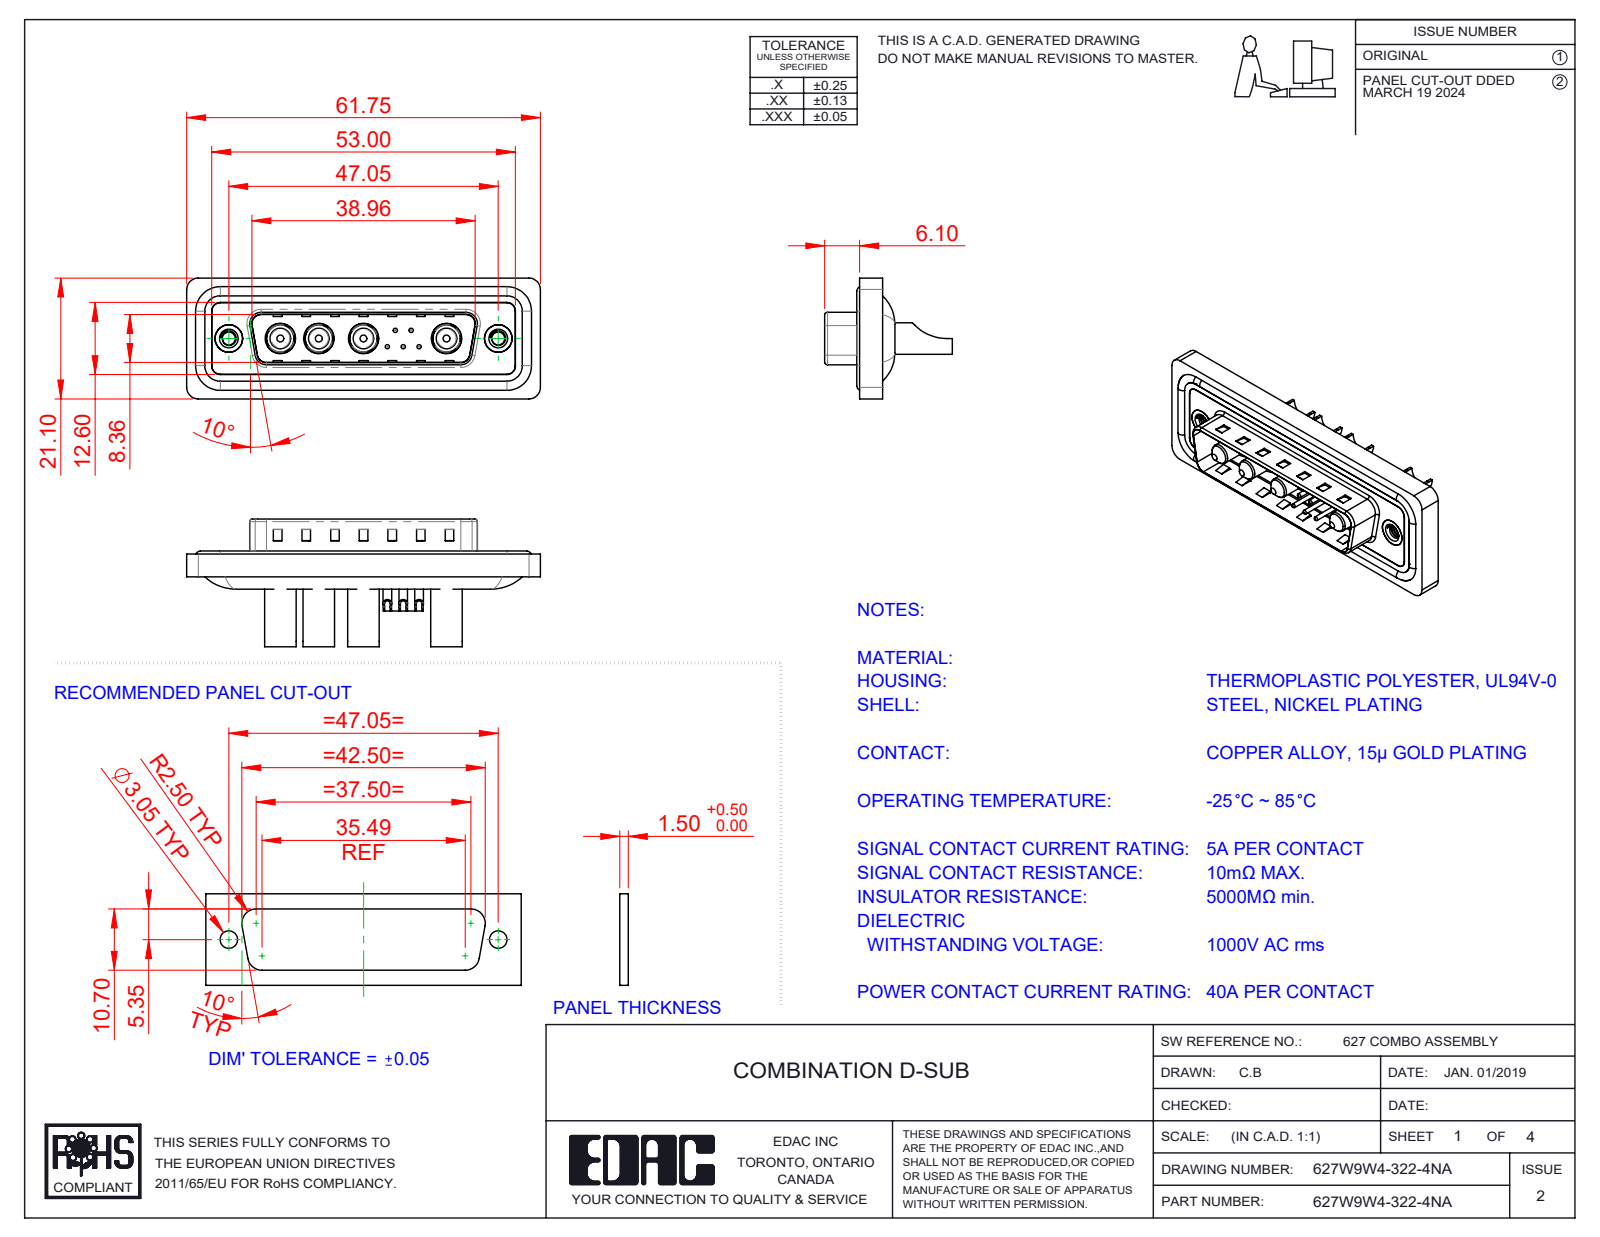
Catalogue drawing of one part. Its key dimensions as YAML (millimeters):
part_name: "627Combo Waterproof Housing_25 Contacts; 627Combo Shell Rear_25 Contacts; Power Pin_40A SC; 627Combo Shell Front_25 Contacts (+5 more)"
step_written_by: "SolidWorks 2023 (CONFIG_CONTROL_DESIGN)"
units: millimeters
bodies: {solids: 20, faces: 838, planar: 302, cylindrical: 350, other: 186}
overall_size: [61.75, 22.3, 21.1]
volume: 7573
surface_area: 12432
round_holes:
  - {diameter: 0.75, count: 5}
  - {diameter: 1, count: 5}
  - {diameter: 1.6, count: 5}
  - {diameter: 2, count: 5}
  - {diameter: 4.6, count: 4}
  - {diameter: 4.85, count: 4}
  - {diameter: 5.3, count: 4}
  - {diameter: 2.26, count: 2}
  - {diameter: 4, count: 2}
  - {diameter: 4.8, count: 2}
  - {diameter: 5, count: 2}
round_bosses_or_shafts:
  - {diameter: 1.5, count: 5}
  - {diameter: 5.5, count: 4}
  - {diameter: 5.2, count: 4}
  - {diameter: 4.75, count: 4}
  - {diameter: 3.75, count: 4}
  - {diameter: 3.6, count: 4}
  - {diameter: 1.6, count: 4}
  - {diameter: 4.9, count: 2}
partial_cylinders:
  - {radius: 1.5, count: 22}
  - {radius: 2, count: 18}
  - {radius: 0.5, count: 8}
  - {radius: 1.6, count: 8}
  - {radius: 1, count: 6}
  - {radius: 0.25, count: 4}
  - {radius: 0.6, count: 4}
  - {radius: 0.65, count: 4}
face_to_face_distances: [0.4, 1.1, 1.5, 0.5, 1.6, 3.1, 2.9, 0.82, 9.58, 5.65]
hole_center_spacings: [3.16, 2.77, 5.04, 14.51, 2.78, 4.4, 4.41, 5]
